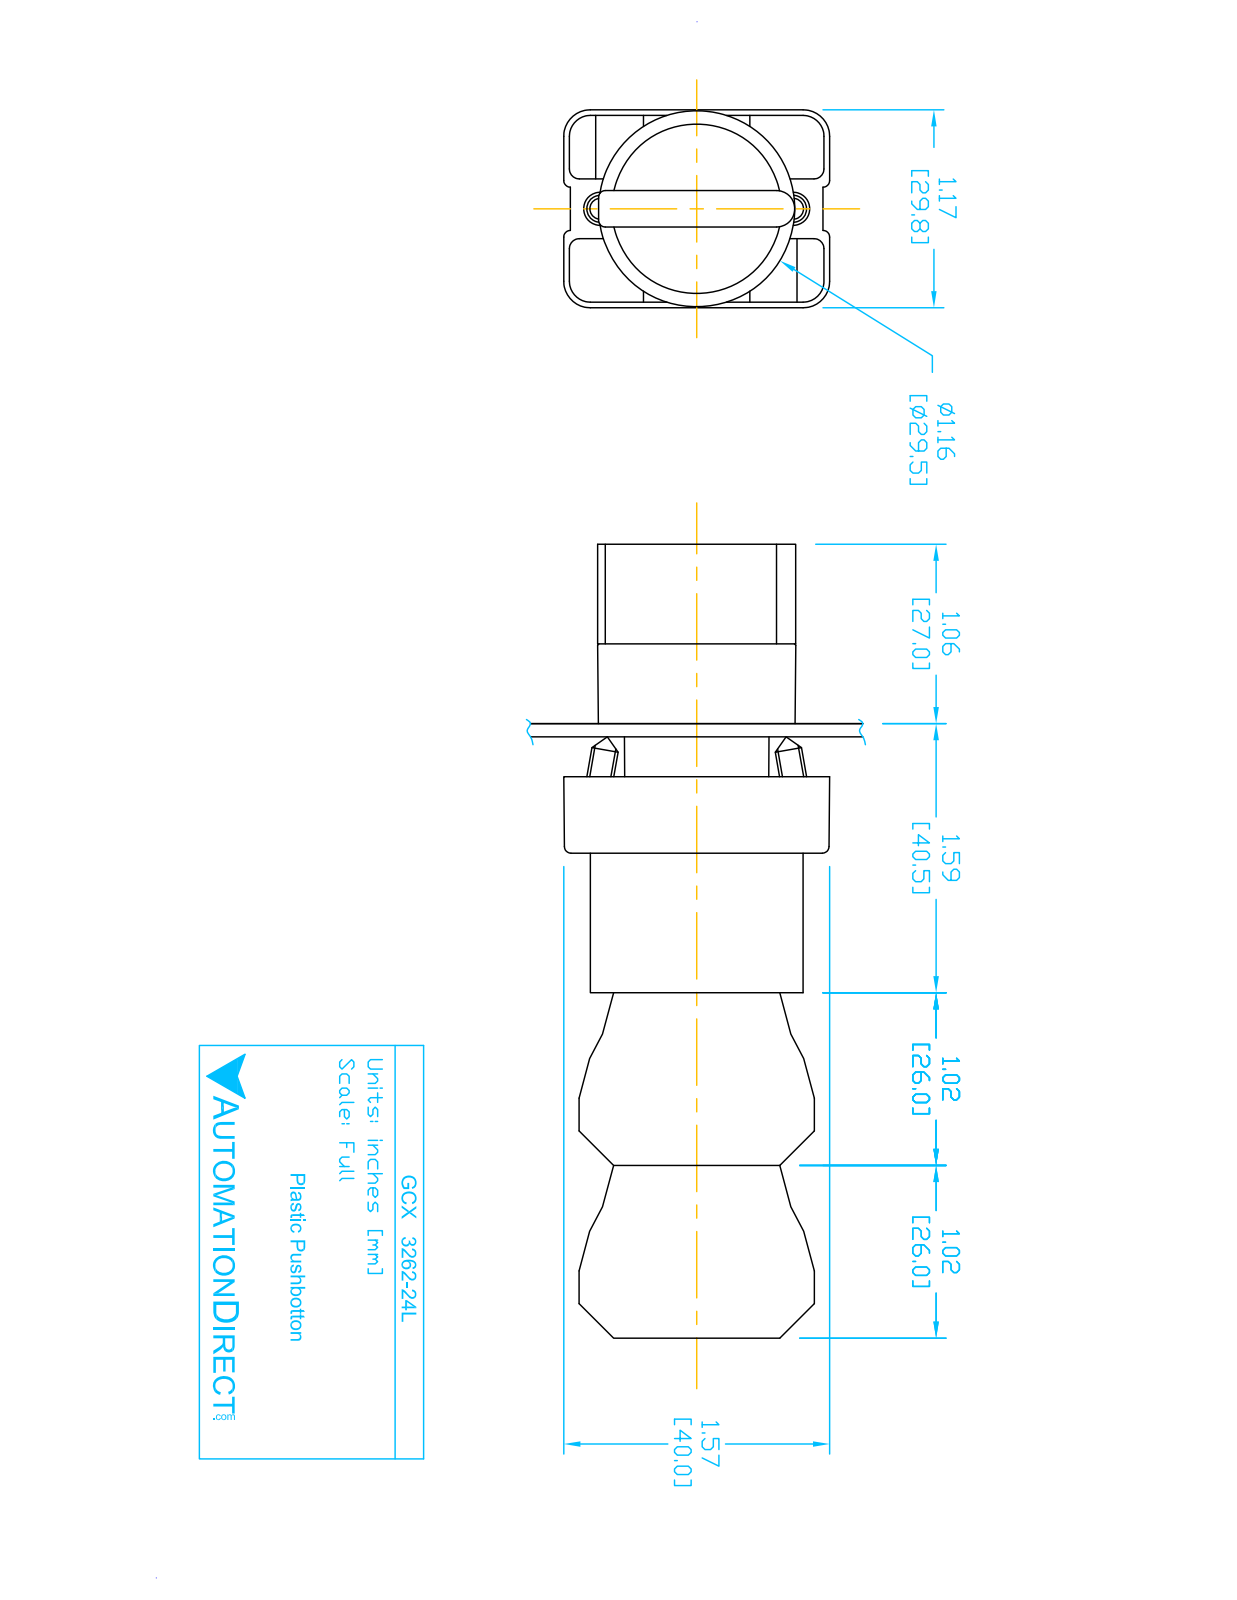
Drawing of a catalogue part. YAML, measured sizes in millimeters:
part_name: "GCX3262L OPERATOR; ecx1030; ecx1040; GCX3262-24L (+2 more)"
step_written_by: "SolidWorks 2016 (AUTOMOTIVE_DESIGN)"
units: millimeters
bodies: {solids: 11, faces: 724, planar: 488, cylindrical: 193, other: 43}
overall_size: [118.8, 40.2, 29.9]
volume: 77850
surface_area: 38210
round_holes:
  - {diameter: 2, count: 4}
  - {diameter: 2.2, count: 2}
  - {diameter: 3.1, count: 2}
  - {diameter: 3.3, count: 2}
  - {diameter: 5, count: 1}
  - {diameter: 11.9, count: 1}
  - {diameter: 22.3, count: 1}
  - {diameter: 22.6, count: 1}
  - {diameter: 26, count: 1}
round_bosses_or_shafts:
  - {diameter: 4, count: 4}
  - {diameter: 29.8, count: 1}
  - {diameter: 25.5, count: 1}
  - {diameter: 24, count: 1}
  - {diameter: 21.7, count: 1}
  - {diameter: 19.8, count: 1}
  - {diameter: 12.8, count: 1}
partial_cylinders:
  - {radius: 1.5, count: 24}
  - {radius: 1, count: 12}
  - {radius: 3.1, count: 12}
  - {radius: 4, count: 12}
  - {radius: 1, count: 9}
  - {radius: 0.5, count: 2}
  - {radius: 1.6, count: 2}
  - {radius: 2, count: 2}
face_to_face_distances: [14.7, 15.1, 26, 29.7, 0.4, 21, 47, 77.3, 51.3, 30.3]
hole_center_spacings: [6, 25.5, 24.7, 12, 13.7, 13.8, 27.5, 12.3]
